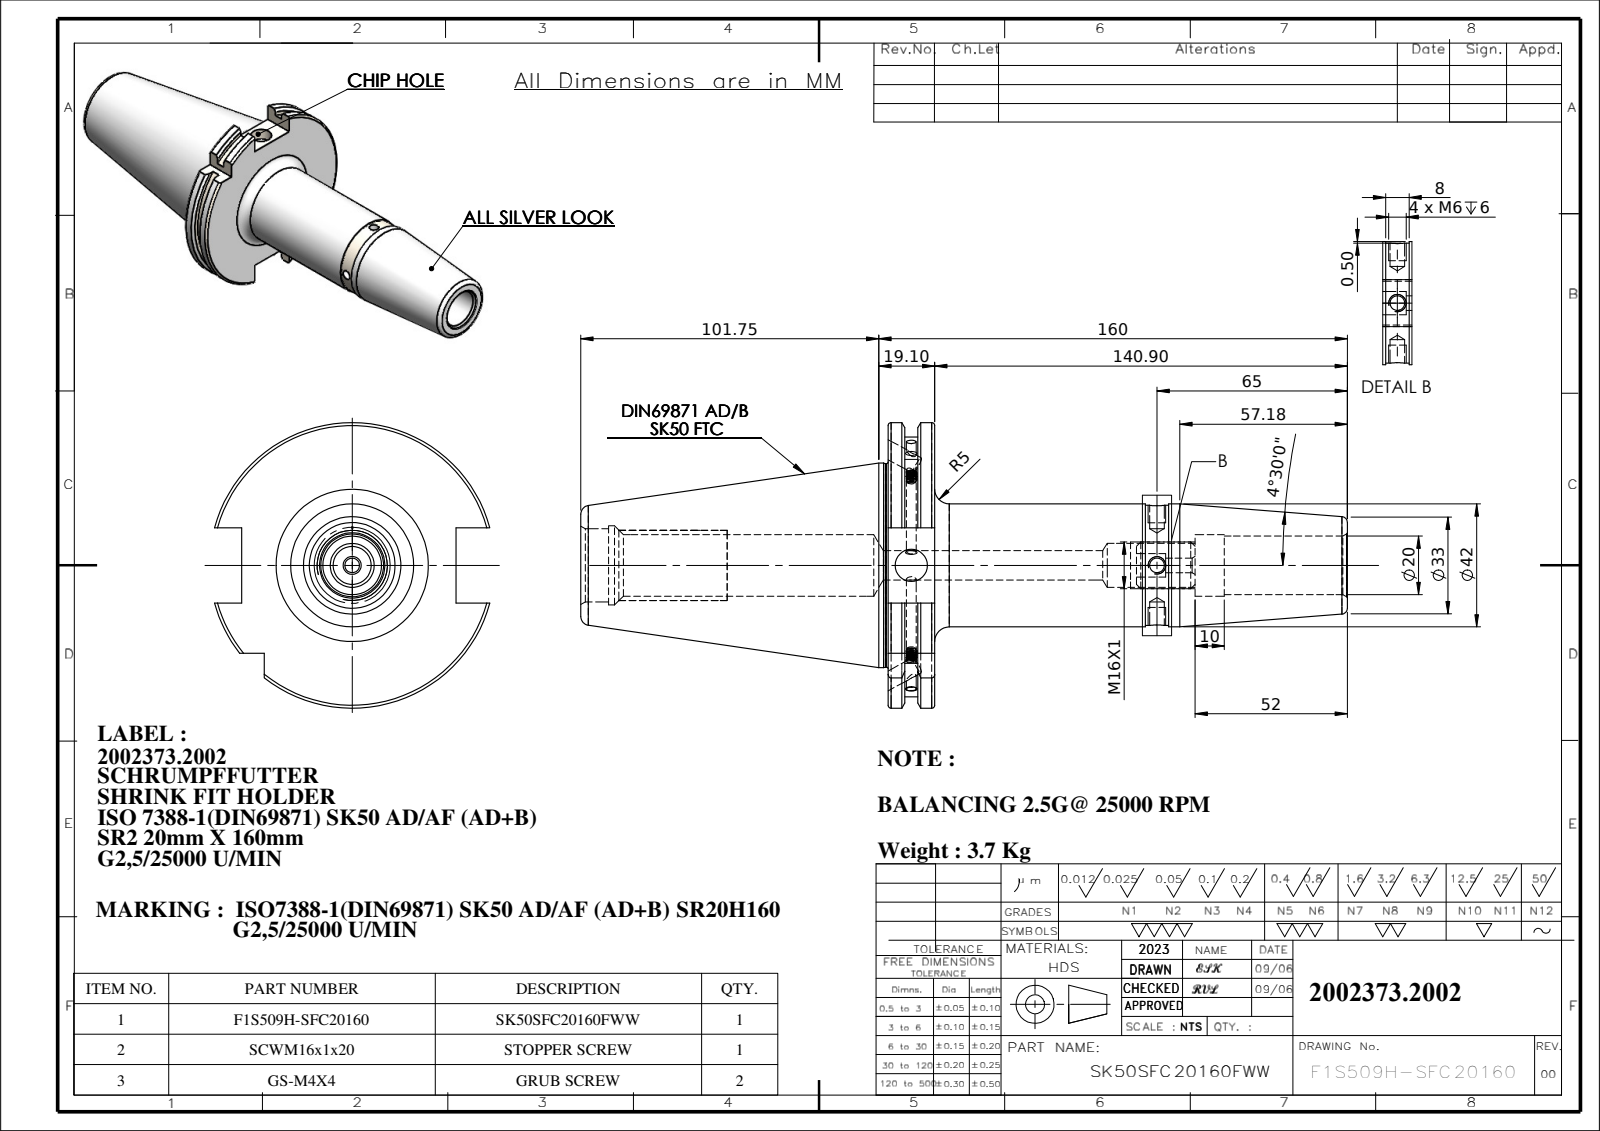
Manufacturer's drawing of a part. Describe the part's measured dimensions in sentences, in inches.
The part is named "SK50SFC20160FWW; GS-M4X4_DIN 913 - M4 x 4-N; SCWM16X1P; 91506-SR220160". Its 3-D file was written by "SolidWorks 2018 (CONFIG_CONTROL_DESIGN)". It is 4 solids with 251 faces: 54 planar, 83 cylindrical and 114 other. Overall it measures 10.305 by 3.839 by 3.703 inches. Its volume is 29.18 cubic inches and its surface area 109.6 square inches. Round holes: 3 of diameter 0.197, 2 of diameter 0.236, 1 of diameter 0.13, 1 of diameter 0.394, 1 of diameter 0.433, 1 of diameter 0.591, 1 of diameter 0.787, 1 of diameter 0.827, 1 of diameter 0.984, 1 of diameter 1.063. Round bosses or shafts: 2 of diameter 0.157, 1 of diameter 2.75, 1 of diameter 2.734, 1 of diameter 1.654, 1 of diameter 1.614, 1 of diameter 0.63. Partial cylindrical surfaces (rounded edges, fillets, slot ends): 1 of radius 1.768, 1 of radius 1.919. The main face-to-face distances are 0.626, 0.223, 0.403, 0.399, 0.176, 0.227, 4.132, 4.355, 4.531, 4.758. The hole center spacings are 3.303.
